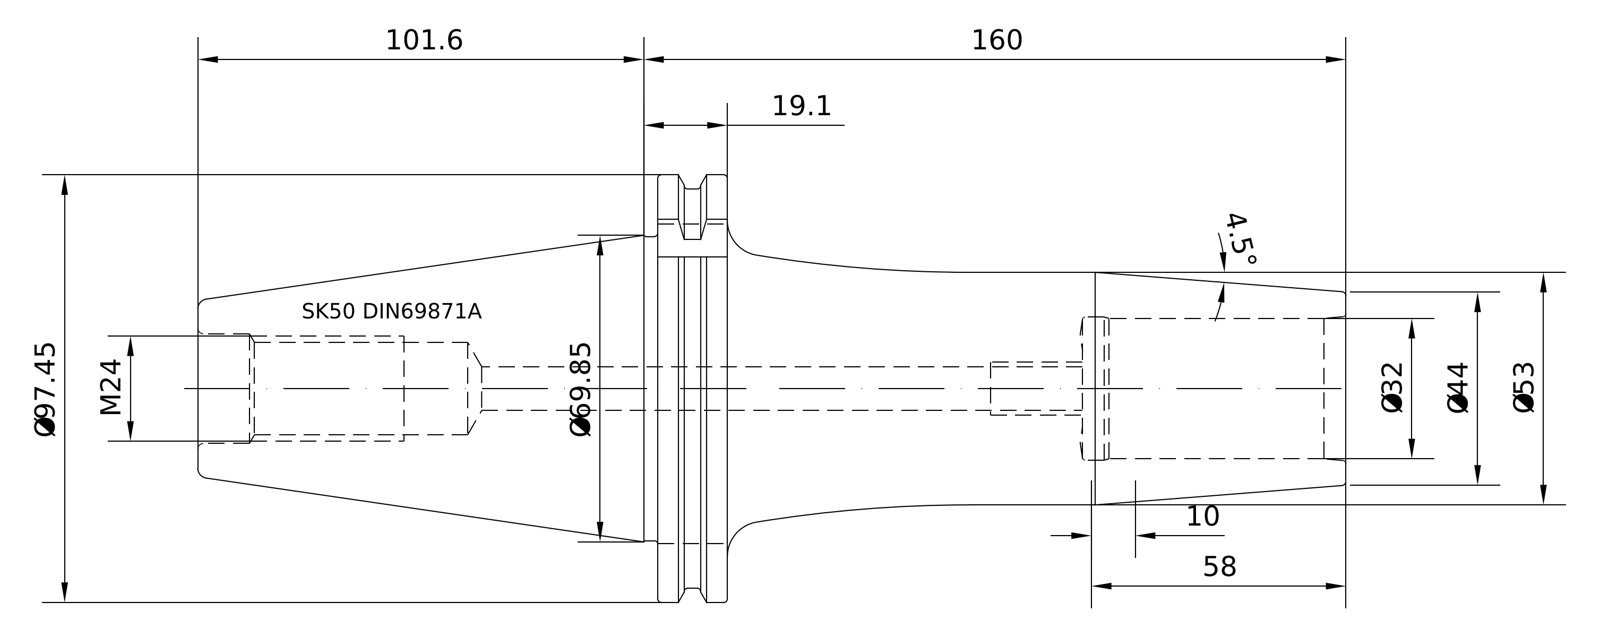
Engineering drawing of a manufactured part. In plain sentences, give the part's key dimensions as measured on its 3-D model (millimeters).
The part is named "50-442-32". Its 3-D file was written by "PRO/ENGINEER BY PARAMETRIC TECHNOLOGY CORPORATION, 2010430 (CONFIG_CONTROL_DESIGN)". It is 1 solid with 96 faces: 22 planar, 24 cylindrical and 50 other. Overall it measures 261.6 by 97.47 by 94 millimeters. Its volume is 601 649 cubic millimeters and its surface area 69 721 square millimeters. Round holes: 1 of diameter 20.75, 1 of diameter 25.01, 1 of diameter 25.7, 1 of diameter 32. Round bosses or shafts: 1 of diameter 91, 1 of diameter 69.15, 1 of diameter 53, 1 of diameter 24.01. Partial cylindrical surfaces (rounded edges, fillets, slot ends): 1 of radius 1.75, 1 of radius 48.74. The main face-to-face distances are 15.85, 98.8, 82.95, 156.8, 140.95, 58, 72.8, 104.8, 120.65, 203.6.
